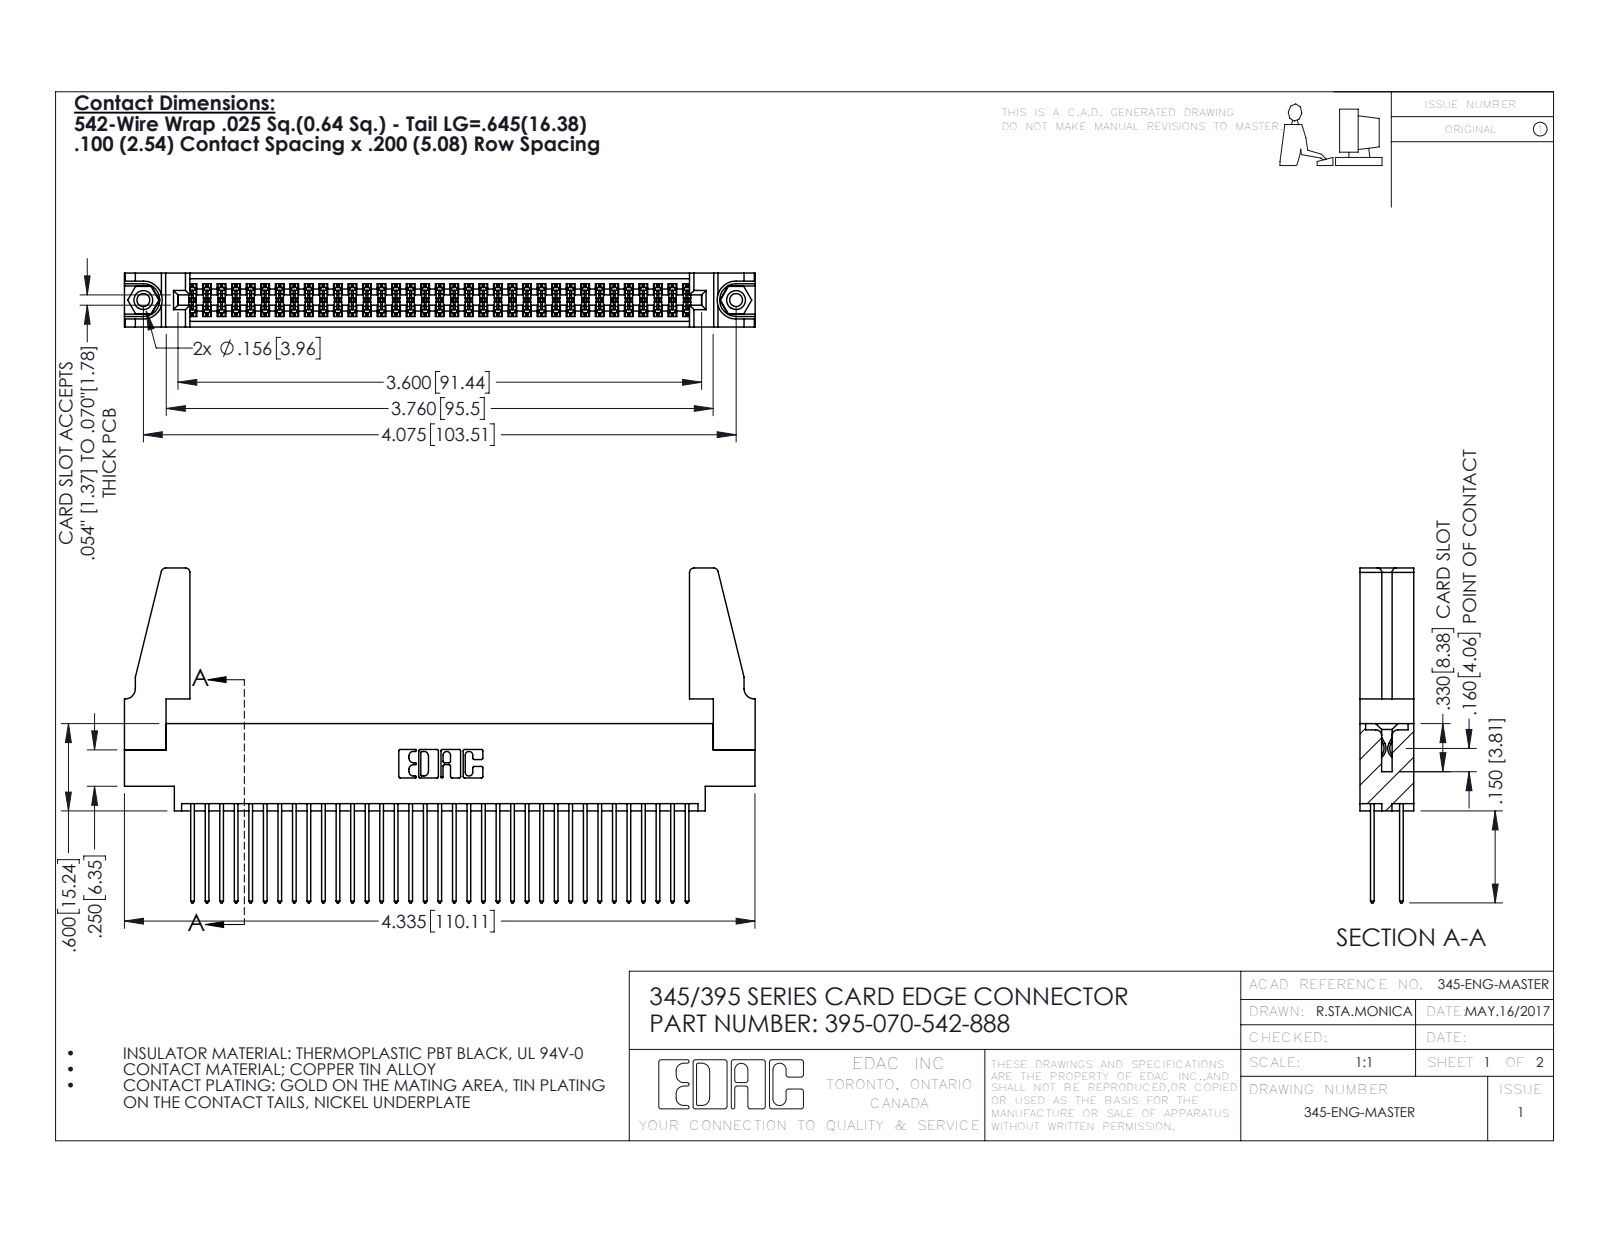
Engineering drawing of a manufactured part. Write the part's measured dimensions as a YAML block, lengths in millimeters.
part_name: "395-070-542-888; 345-292-001_345-293-142; 345-220-078_345-220-088; 345 Part_0.170 Offset - 0.156 Dia-TH (+1 more)"
step_written_by: "SolidWorks 2016 (CONFIG_CONTROL_DESIGN)"
units: millimeters
bodies: {solids: 75, faces: 3754, planar: 2466, cylindrical: 1272, other: 16}
overall_size: [110.1, 58.5, 9.4]
volume: 14100
surface_area: 20690
round_holes:
  - {diameter: 2.3, count: 2}
  - {diameter: 3.2, count: 2}
  - {diameter: 4, count: 2}
  - {diameter: 1.6, count: 1}
round_bosses_or_shafts:
  - {diameter: 3.9, count: 2}
partial_cylinders:
  - {radius: 0.2, count: 105}
  - {radius: 0.3, count: 70}
  - {radius: 0.3, count: 22}
  - {radius: 0.8, count: 8}
  - {radius: 0.2, count: 6}
  - {radius: 0.8, count: 6}
  - {radius: 0.7, count: 3}
  - {radius: 0.4, count: 2}
face_to_face_distances: [1.8, 7.6, 9.4, 2.5, 6.9, 0.6, 5.1, 5.7, 4.4, 3.8]
hole_center_spacings: [6.9, 97.5, 103.5]
